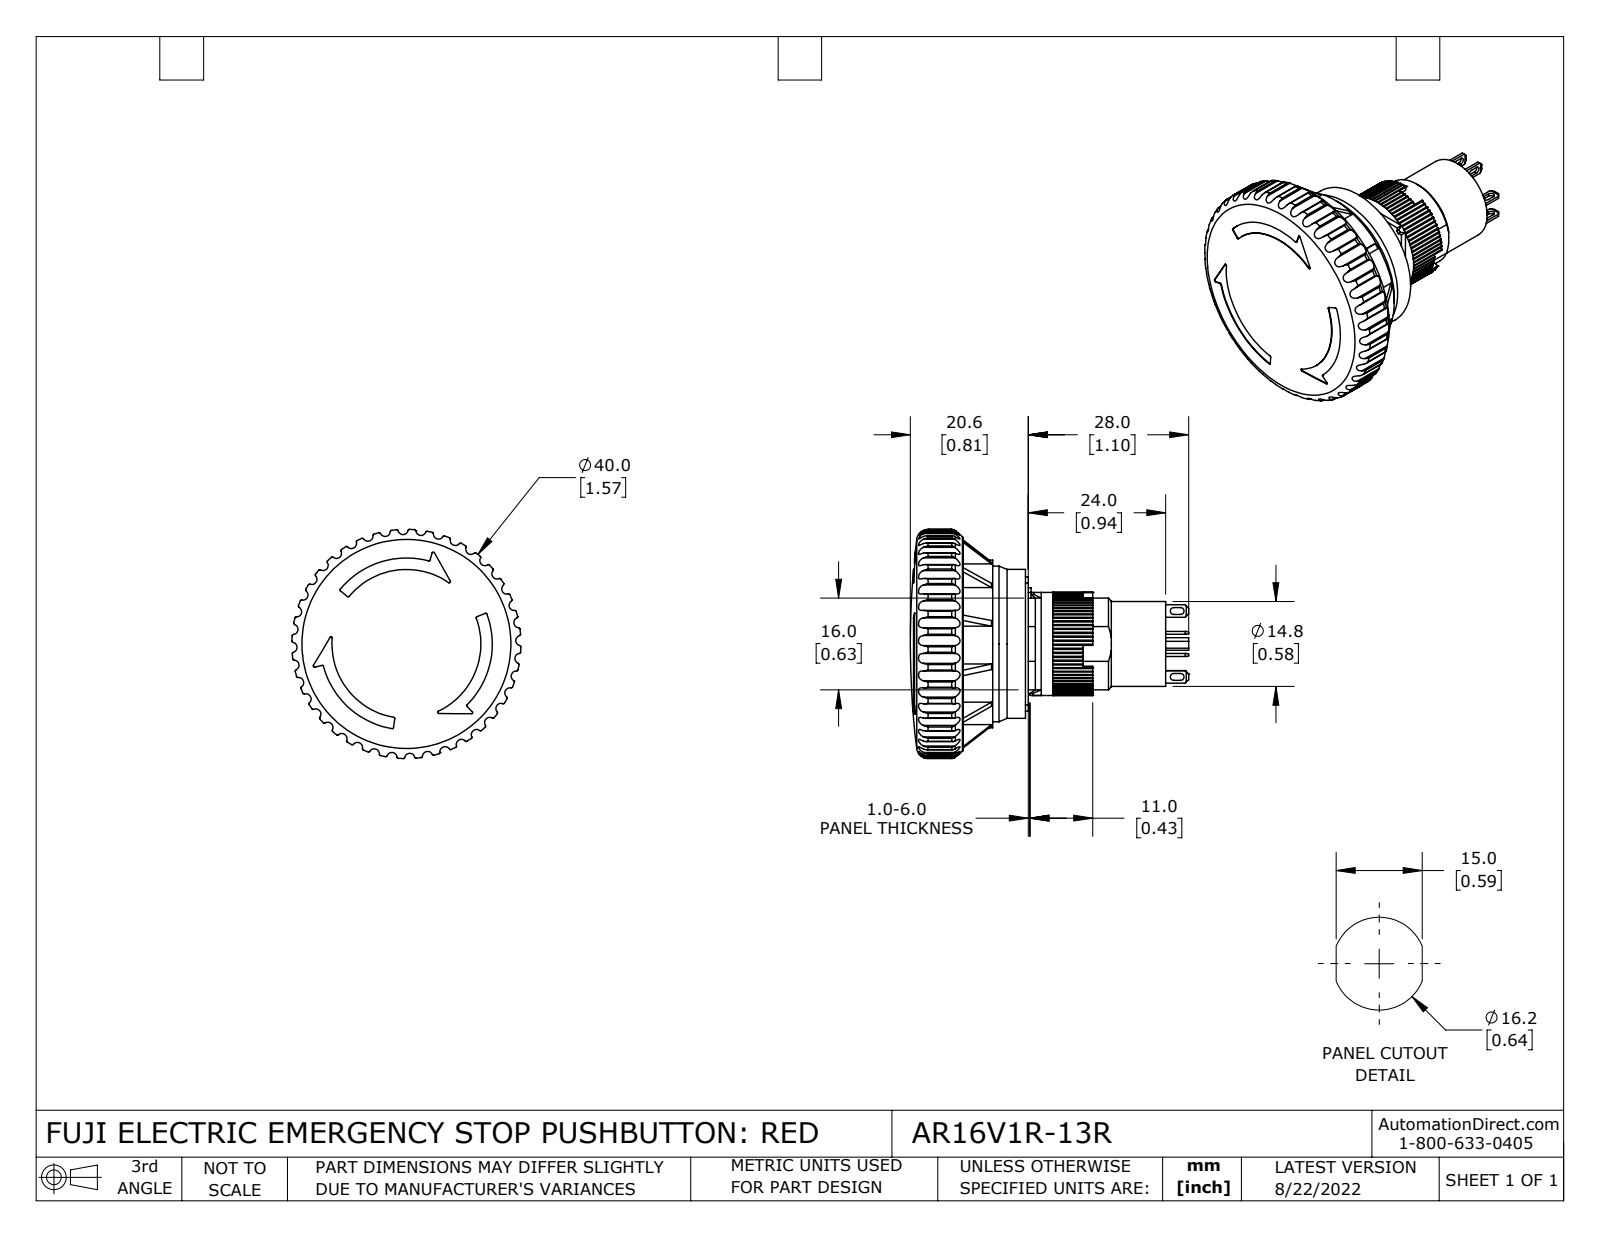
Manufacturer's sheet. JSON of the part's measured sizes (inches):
{"part_name": "AR16V1R-13R", "step_written_by": "SolidWorks 2021 (CONFIG_CONTROL_DESIGN)", "units": "inches", "bodies": {"solids": 5, "faces": 1001, "planar": 495, "cylindrical": 410, "other": 96}, "overall_size": [1.913, 1.575, 1.575], "volume_in3": 0.963, "surface_area_in2": 19.04, "round_holes": [[0.583, 1], [0.63, 1], [0.709, 1], [1.069, 1], [1.433, 1]], "round_bosses_or_shafts": [[1.154, 1], [1.024, 1], [0.858, 1], [0.236, 1]], "partial_cylinders_radius": [[0.008, 80], [0.01, 80], [0.035, 40], [0.02, 8], [0.024, 8], [0.039, 2], [0.031, 1], [0.114, 1]], "face_to_face_distances": [0.039, 0.421, 0.53, 0.108, 0.02, 0.069, 0.856, 0.49, 0.089, 0.049]}
